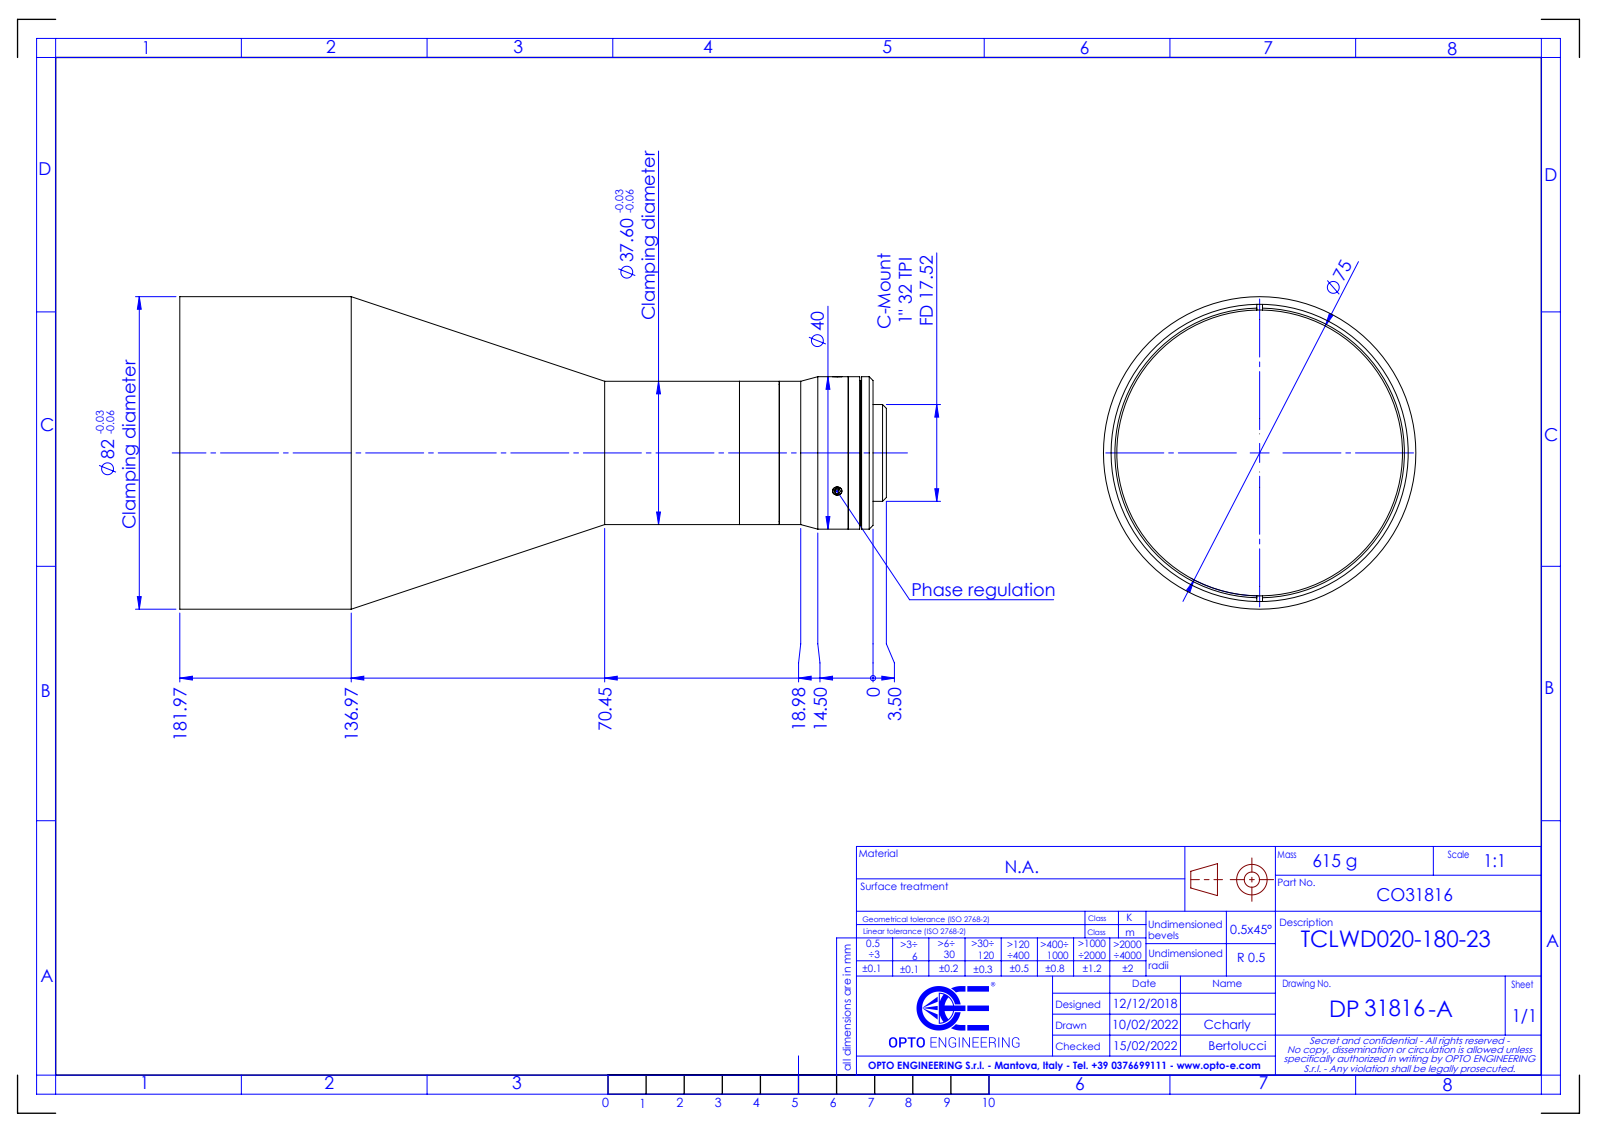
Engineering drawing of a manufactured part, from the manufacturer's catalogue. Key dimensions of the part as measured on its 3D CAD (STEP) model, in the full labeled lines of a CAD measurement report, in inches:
Part name (STEP PRODUCT): DP31816-A_TCLWD020-180-23
STEP written by: SolidWorks 2021 (CONFIG_CONTROL_DESIGN)
Units: inches
Bodies: 0 solids, 85 faces (38 planar, 28 cylindrical, 19 other)
Overall size (bounding box): 7.302 × 3.228 × 3.228
Round holes (diameter × count): ⌀0.098 ×2, ⌀0.886 ×1, ⌀1.004 ×1, ⌀2.953 ×1, ⌀3.071 ×1
Round bosses / shafts (diameter × count): ⌀3.228 ×1, ⌀1.575 ×1, ⌀1.48 ×1, ⌀1 ×1
Main face-to-face distances: 0.138, 0.118, 0.02, 0.256, 0.413, 0.276, 0.394, 0.531, 6.633, 6.908
